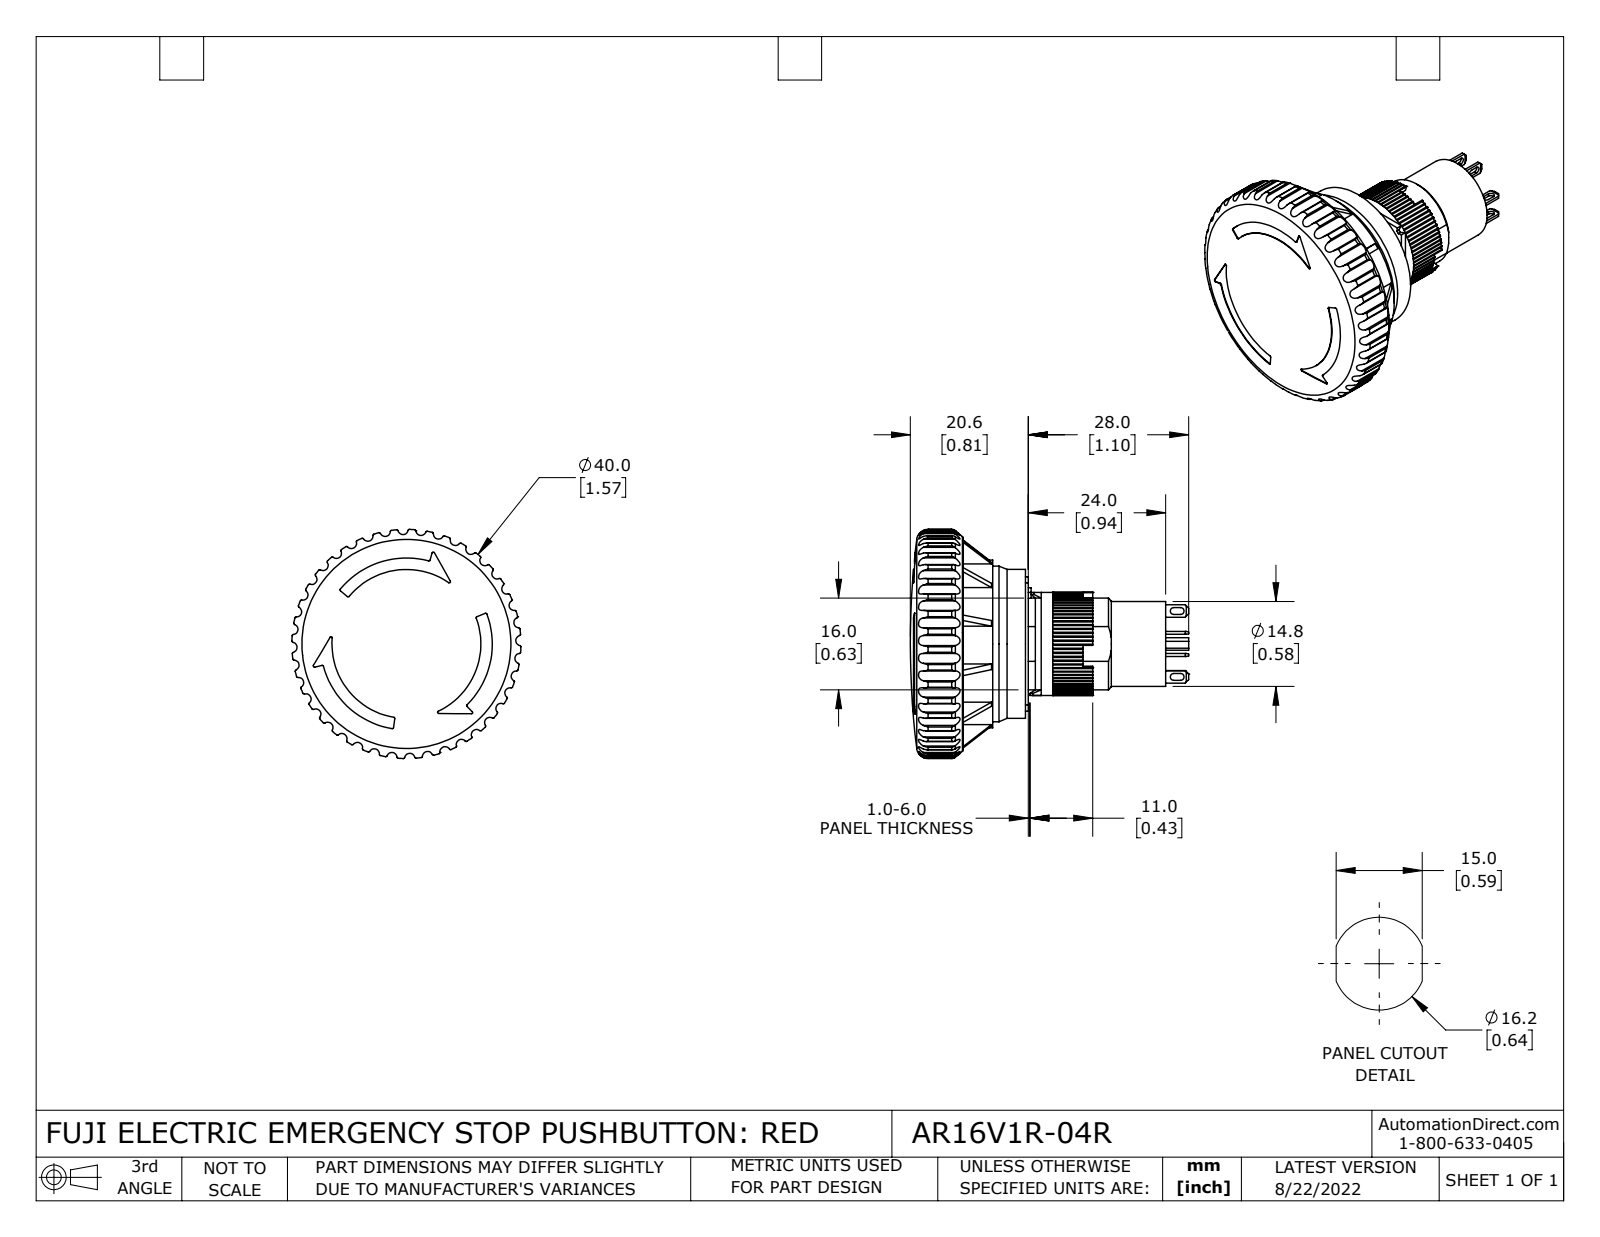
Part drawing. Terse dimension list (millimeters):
name: AR16V1R-04R
written by: SolidWorks 2021 (CONFIG_CONTROL_DESIGN)
unit: mm
bodies: 5 solids, 1001 faces (495 planar, 410 cylindrical, 96 other)
size: 48.6 × 40 × 40
volume: 15 800 mm³; area: 12 280 mm²
holes: 1× ⌀14.8, 1× ⌀16, 1× ⌀18, 1× ⌀27.2, 1× ⌀36.4
bosses: 1× ⌀29.3, 1× ⌀26, 1× ⌀21.8, 1× ⌀6
rounds: 80× R0.2, 80× R0.3, 40× R0.9, 8× R0.5, 8× R0.6, 2× R1, 1× R0.8, 1× R2.9
face distances: 1, 10.7, 13.5, 2.7, 0.5, 1.8, 21.7, 12.4, 2.3, 1.2
